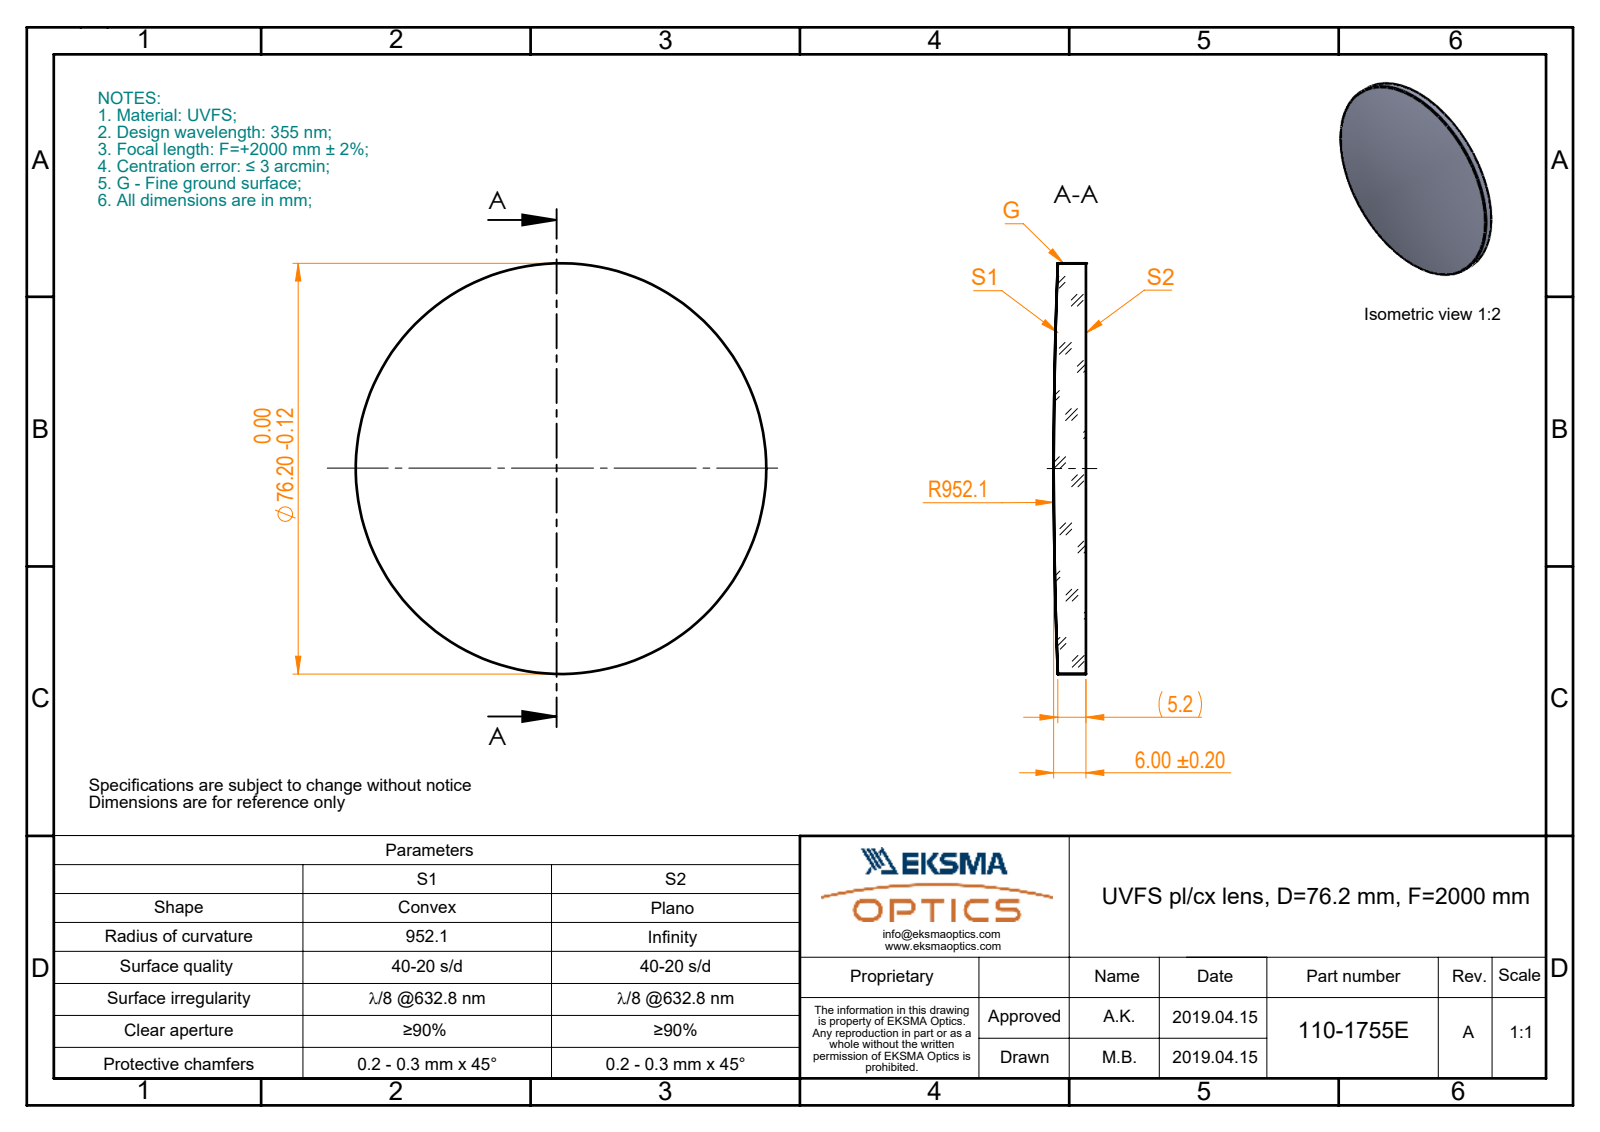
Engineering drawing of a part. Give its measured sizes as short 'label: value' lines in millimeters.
name: 110-1755E UVFS pl-cx 76.2 F2000
written by: SolidWorks 2017 (CONFIG_CONTROL_DESIGN)
unit: mm
bodies: 1 solid, 5 faces (1 planar, 2 cylindrical, 2 other)
size: 76.2 × 76.2 × 6
volume: 25 624 mm³; area: 10 376 mm²
bosses: 1× ⌀76.2
